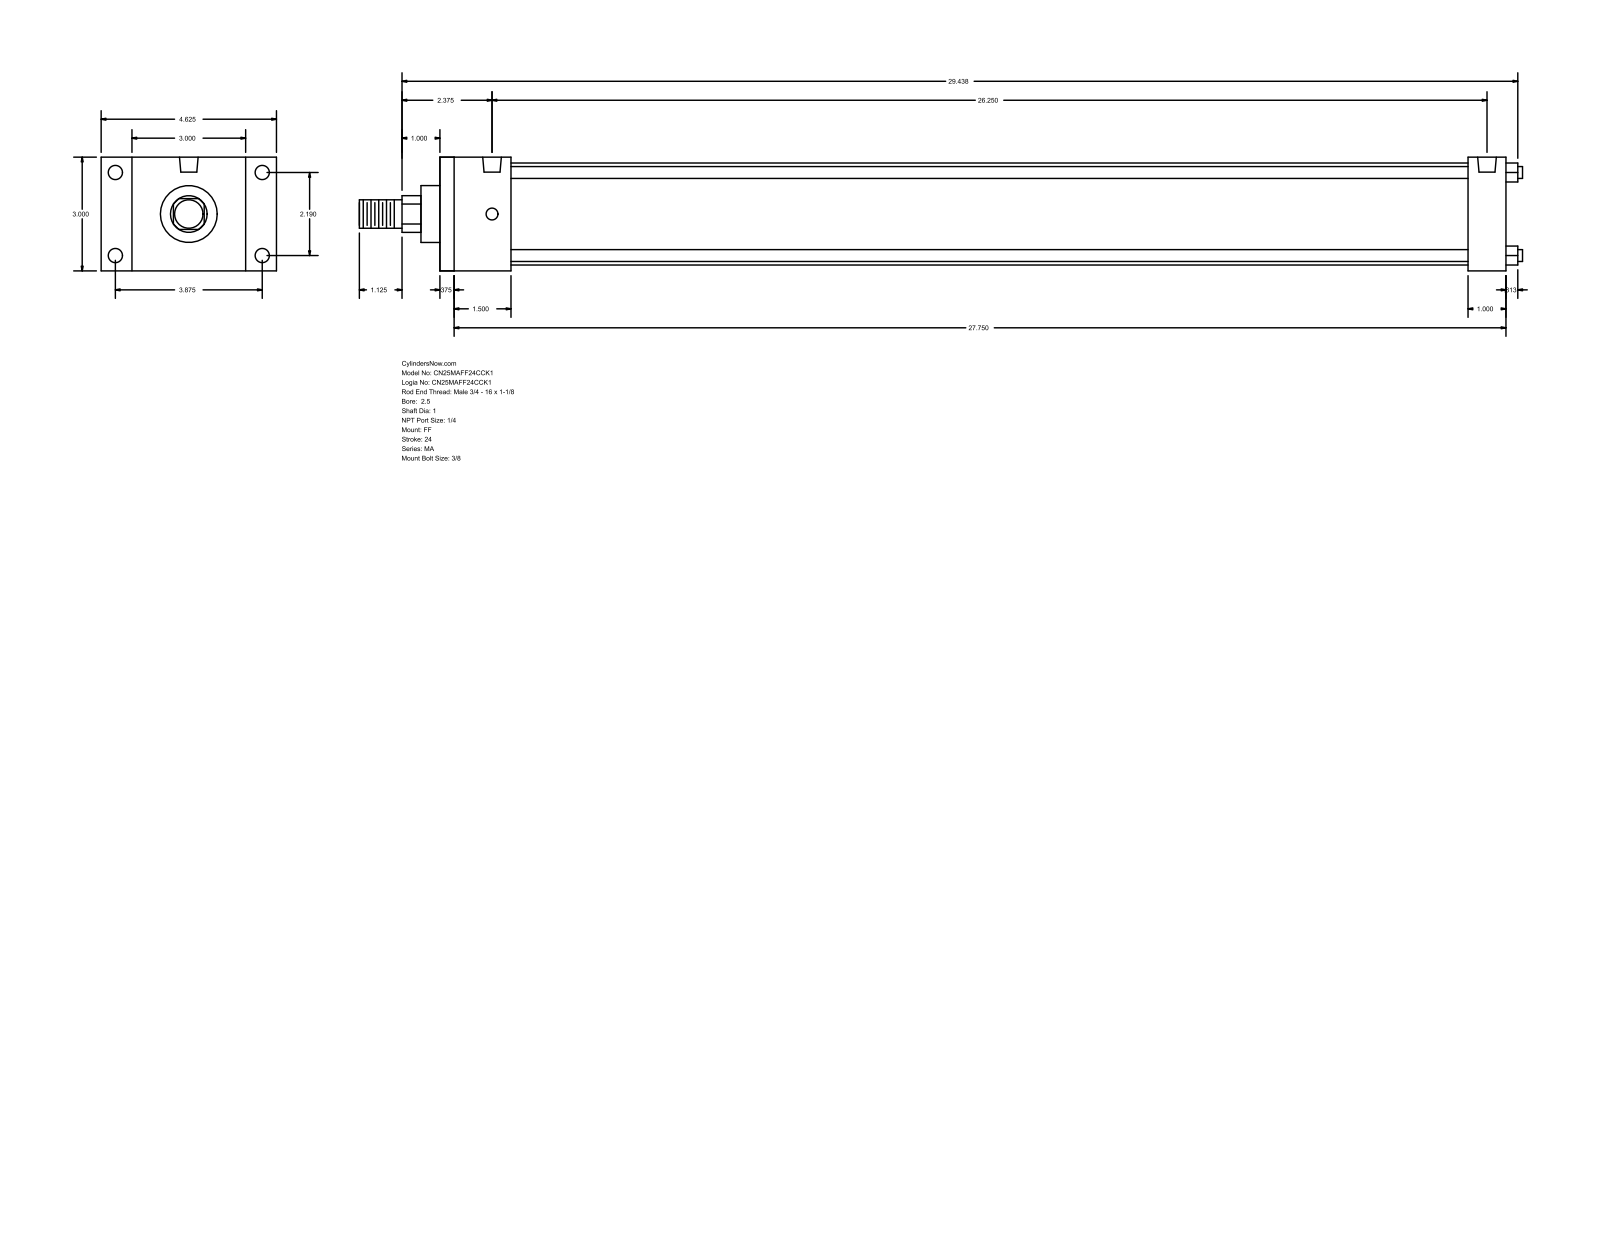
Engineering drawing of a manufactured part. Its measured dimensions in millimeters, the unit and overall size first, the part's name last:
Units: millimetres
Overall size (bounding box): 779.46 × 117.47 × 76.2
Round holes (diameter × count): ⌀7.94 ×4, ⌀9.53 ×4, ⌀12.49 ×2
Round bosses / shafts (diameter × count): ⌀7.94 ×4, ⌀68.33 ×1, ⌀38.1 ×1, ⌀25.4 ×1, ⌀19.05 ×1
Partial cylindrical surfaces — rounded edges, fillets, slot ends (radius × count): R12.29 ×1
Main face-to-face distances: 76.2, 714.37, 704.85, 9.52, 25.39, 47.63, 688.98, 38.11, 679.46, 641.35
Hole centre spacings: 55.62, 98.42, 113.05, 666.75
Bodies: 0 solids, 92 faces (64 planar, 28 cylindrical, 0 other)
Part name (STEP PRODUCT): MA_FF__0250_1
STEP written by: GSSL Pune (CONFIG_CONTROL_DESIGN)
